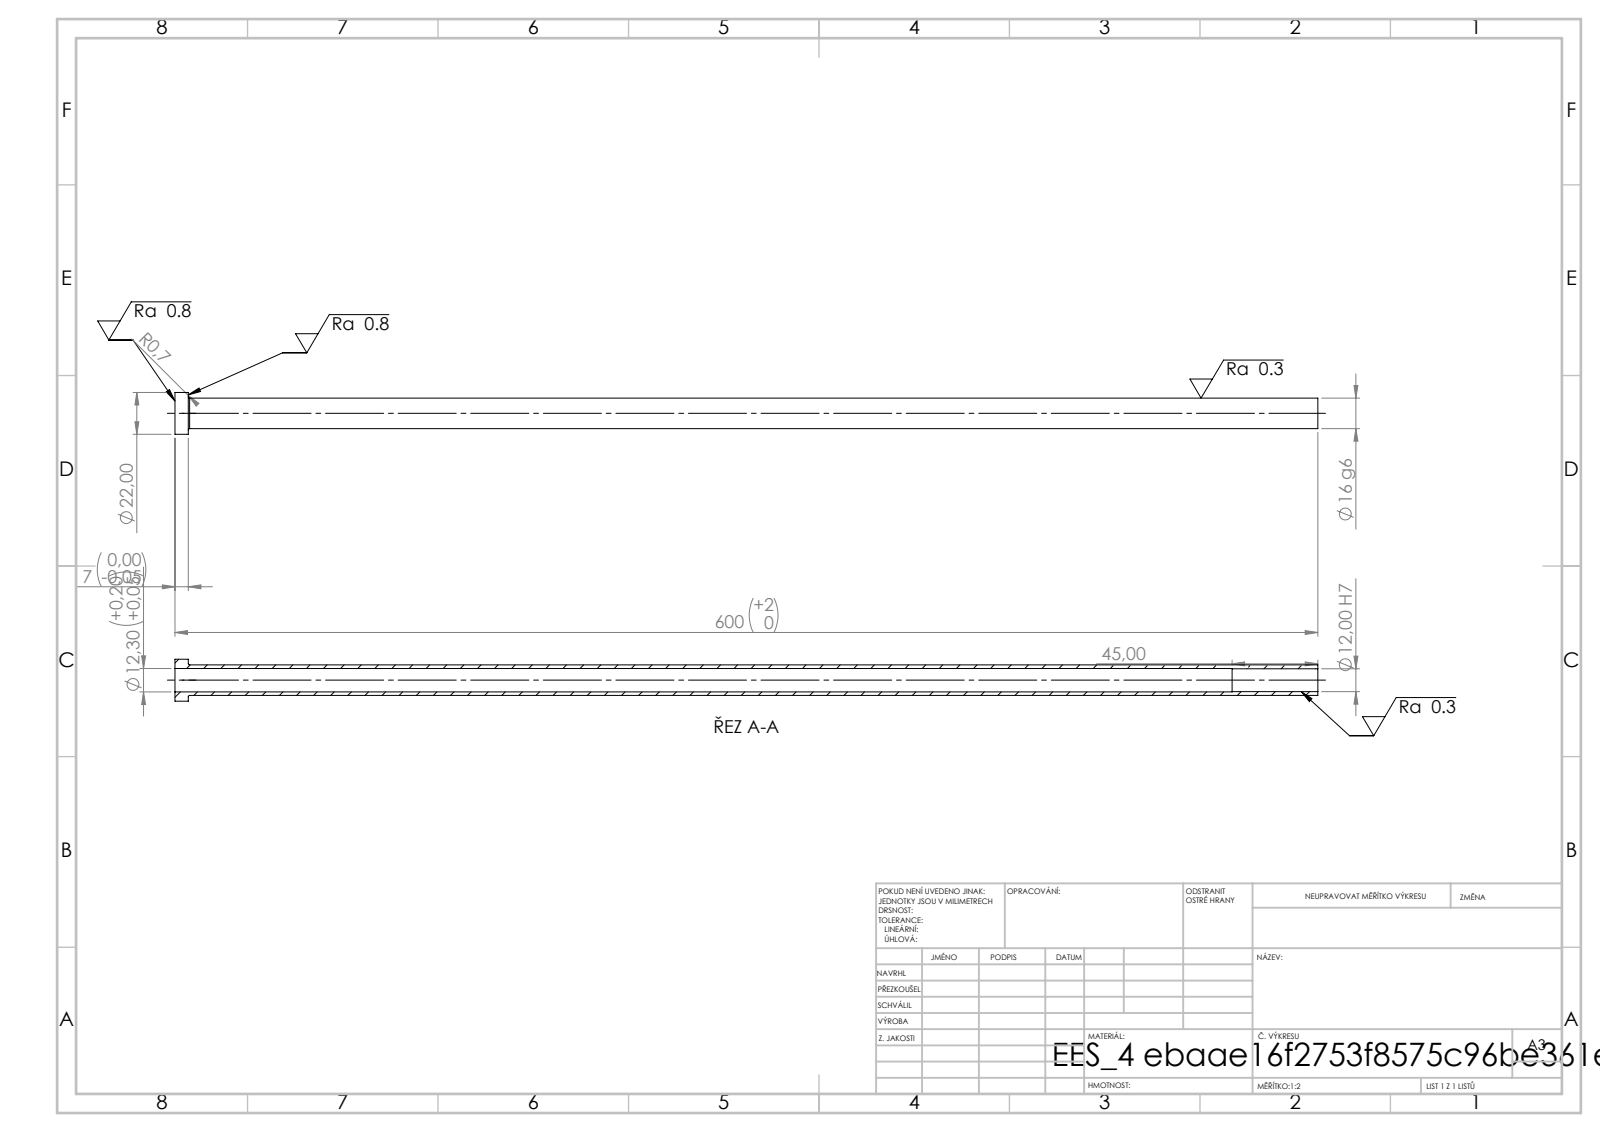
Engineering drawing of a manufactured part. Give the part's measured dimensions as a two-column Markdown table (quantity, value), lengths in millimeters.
| quantity | value |
| --- | --- |
| STEP written by | SolidWorks 2019 (CONFIG_CONTROL_DESIGN) |
| units | millimeters |
| bodies | 1 solid, 14 faces (4 planar, 8 cylindrical, 2 other) |
| overall size | 600 × 22 × 22 |
| volume | 50 860 mm³ |
| surface area | 53 953 mm² |
| round holes (diameter × count) | 12 × 1, 12.3 × 1 |
| round bosses / shafts (diameter × count) | 22 × 1, 16 × 1 |
| main face-to-face distances | 7, 600, 593, 555, 548, 45 |
